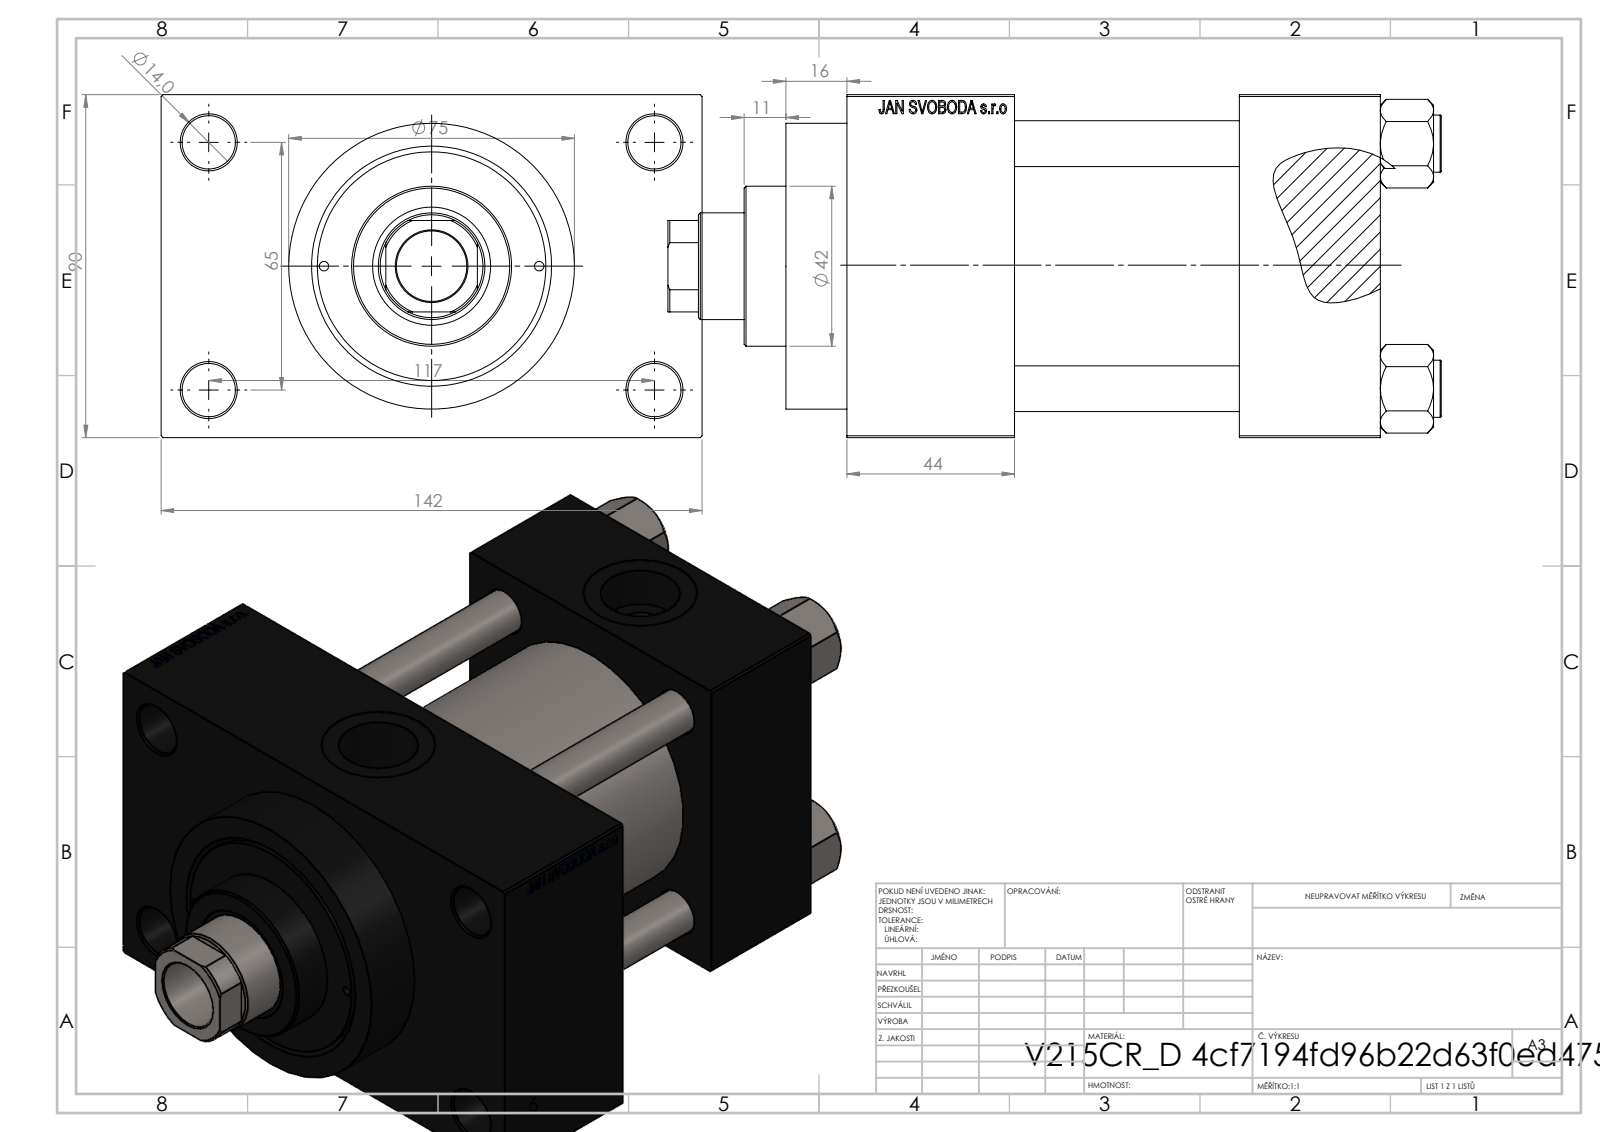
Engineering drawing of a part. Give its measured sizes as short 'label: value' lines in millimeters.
name: V215CR_D_Body; NUT_M5_D; V215_VC_A; V215CR_VCP_D (+1 more)
written by: SolidWorks 2019 (CONFIG_CONTROL_DESIGN)
unit: mm
bodies: 11 solids, 1112 faces (499 planar, 93 cylindrical, 520 other)
size: 203 × 142 × 90
volume: 1 105 000 mm³; area: 198 523 mm²
holes: 4× ⌀12, 4× ⌀14, 2× ⌀2.5, 2× ⌀7, 2× ⌀20.96, 2× ⌀30, 1× ⌀18.5, 1× ⌀28, 1× ⌀31, 1× ⌀50, 1× ⌀60, 1× ⌀63
bosses: 4× ⌀15, 1× ⌀75, 1× ⌀69, 1× ⌀42
rounds: 1× R13.5
face distances: 90, 59, 37, 96, 140, 103, 44, 26, 116, 142
hole spacings: 26.35, 32.39, 44.4, 45.47, 64.3, 66.92, 68.42, 69.81
